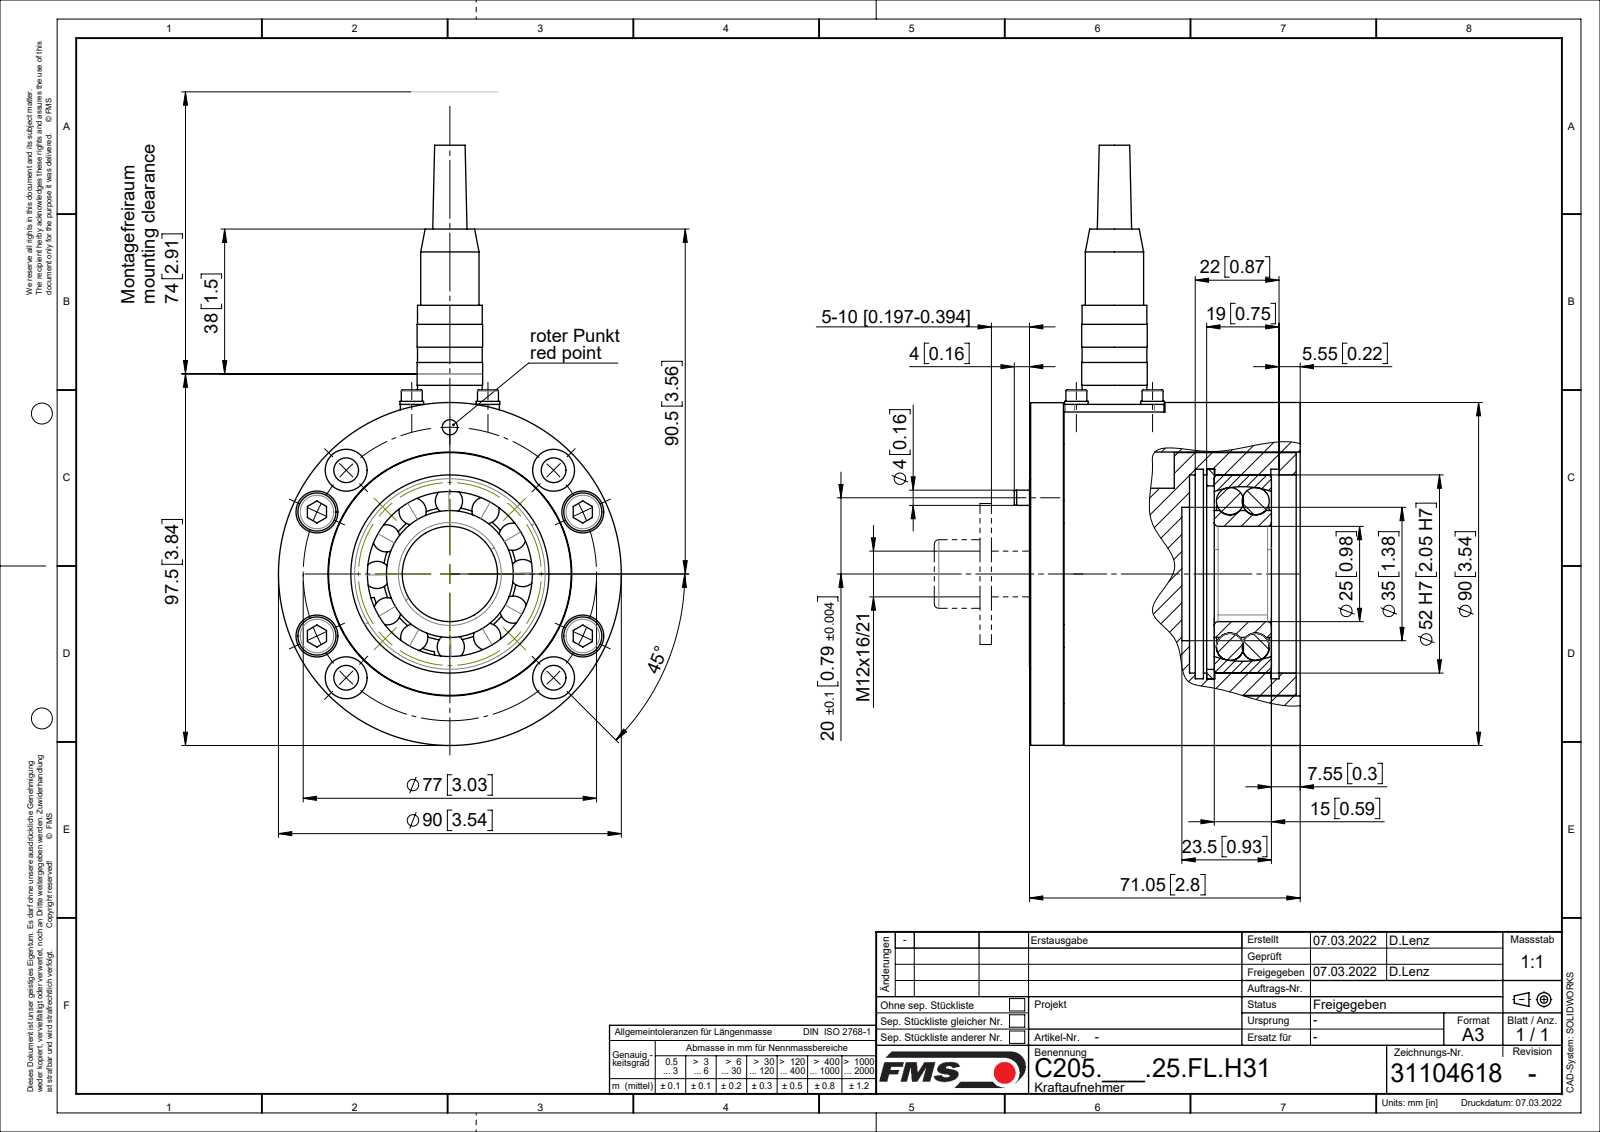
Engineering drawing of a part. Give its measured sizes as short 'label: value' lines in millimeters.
name: Si-Ring DIN472_D52x2; 31104488_01; Federringe_DIN127A_M03; PKL_1205_01 (+8 more)
written by: SolidWorks 2018 (CONFIG_CONTROL_DESIGN)
unit: mm
bodies: 47 solids, 599 faces (185 planar, 256 cylindrical, 158 other)
size: 157.5 × 96.05 × 90
volume: 318 683 mm³; area: 125 368 mm²
holes: 8× ⌀6.5, 8× ⌀11, 6× ⌀2.5, 4× ⌀3.1, 4× ⌀3.2, 4× ⌀5, 4× ⌀7, 2× ⌀4, 1× ⌀3, 1× ⌀10.2, 1× ⌀12, 1× ⌀13
bosses: 5× ⌀1.5, 4× ⌀10, 4× ⌀6.2, 4× ⌀6, 4× ⌀5.5, 4× ⌀3, 1× ⌀90, 1× ⌀89.9
rounds: 4× R0.1, 4× R2.5, 2× R0.5, 2× R4.24, 2× R5, 1× R20.8, 1× R24.1
face distances: 6, 2, 6.5, 32, 25.5, 33.05, 38, 8.6, 29.1, 37.7
hole spacings: 20, 38.5, 13.37, 14.14, 38.49, 44.16, 54.44, 63.07
